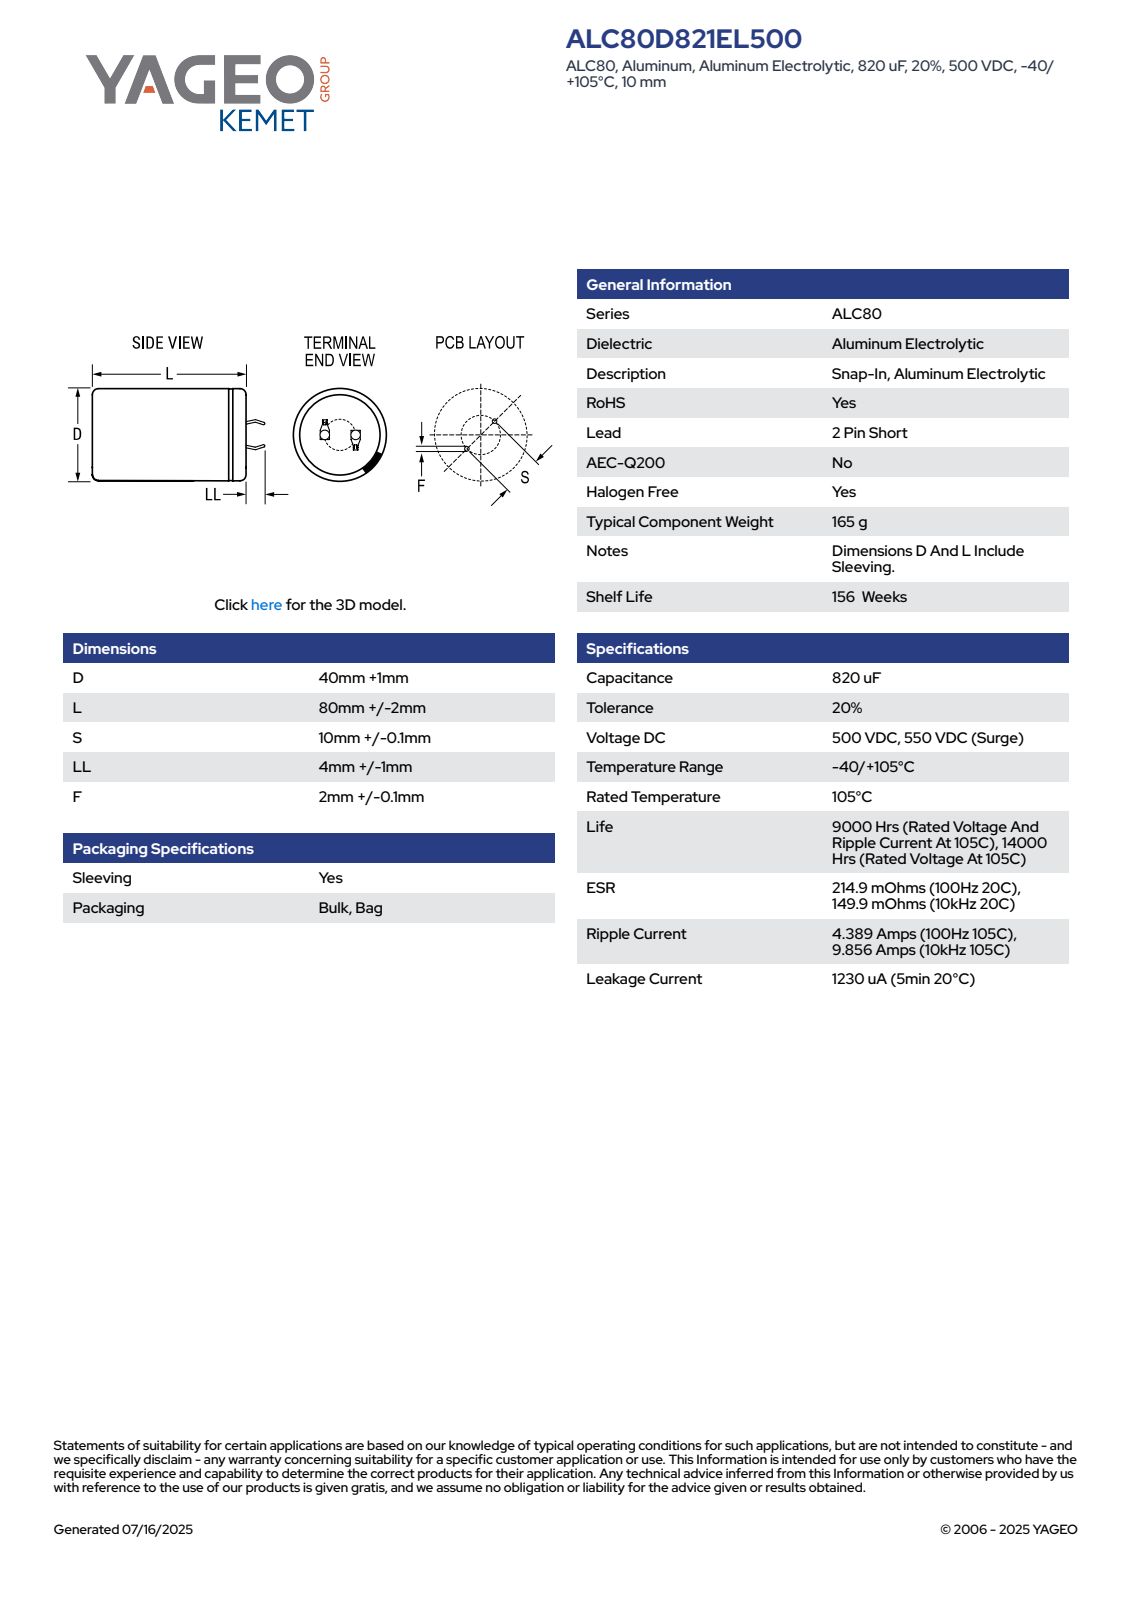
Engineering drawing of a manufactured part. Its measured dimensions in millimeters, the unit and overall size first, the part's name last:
Units: millimetres
Overall size (bounding box): 86.99 × 41 × 41
Round holes (diameter × count): ⌀36.28 ×1
Round bosses / shafts (diameter × count): ⌀41 ×1
Partial cylindrical surfaces — rounded edges, fillets, slot ends (radius × count): R20.49 ×1
Main face-to-face distances: 81.99, 82.49, 0.5, 7.08, 0.6, 0.59, 7.6, 0.75, 1.35, 7.68
Volume: 107 474 mm³ · Surface area: 13 174 mm²
Bodies: 1 solid, 100 faces (52 planar, 9 cylindrical, 39 other)
Part name (STEP PRODUCT): CARS_K2P_40X80_D41L82S10LL5F2.1
STEP written by: SolidWorks 2014 (AUTOMOTIVE_DESIGN)
